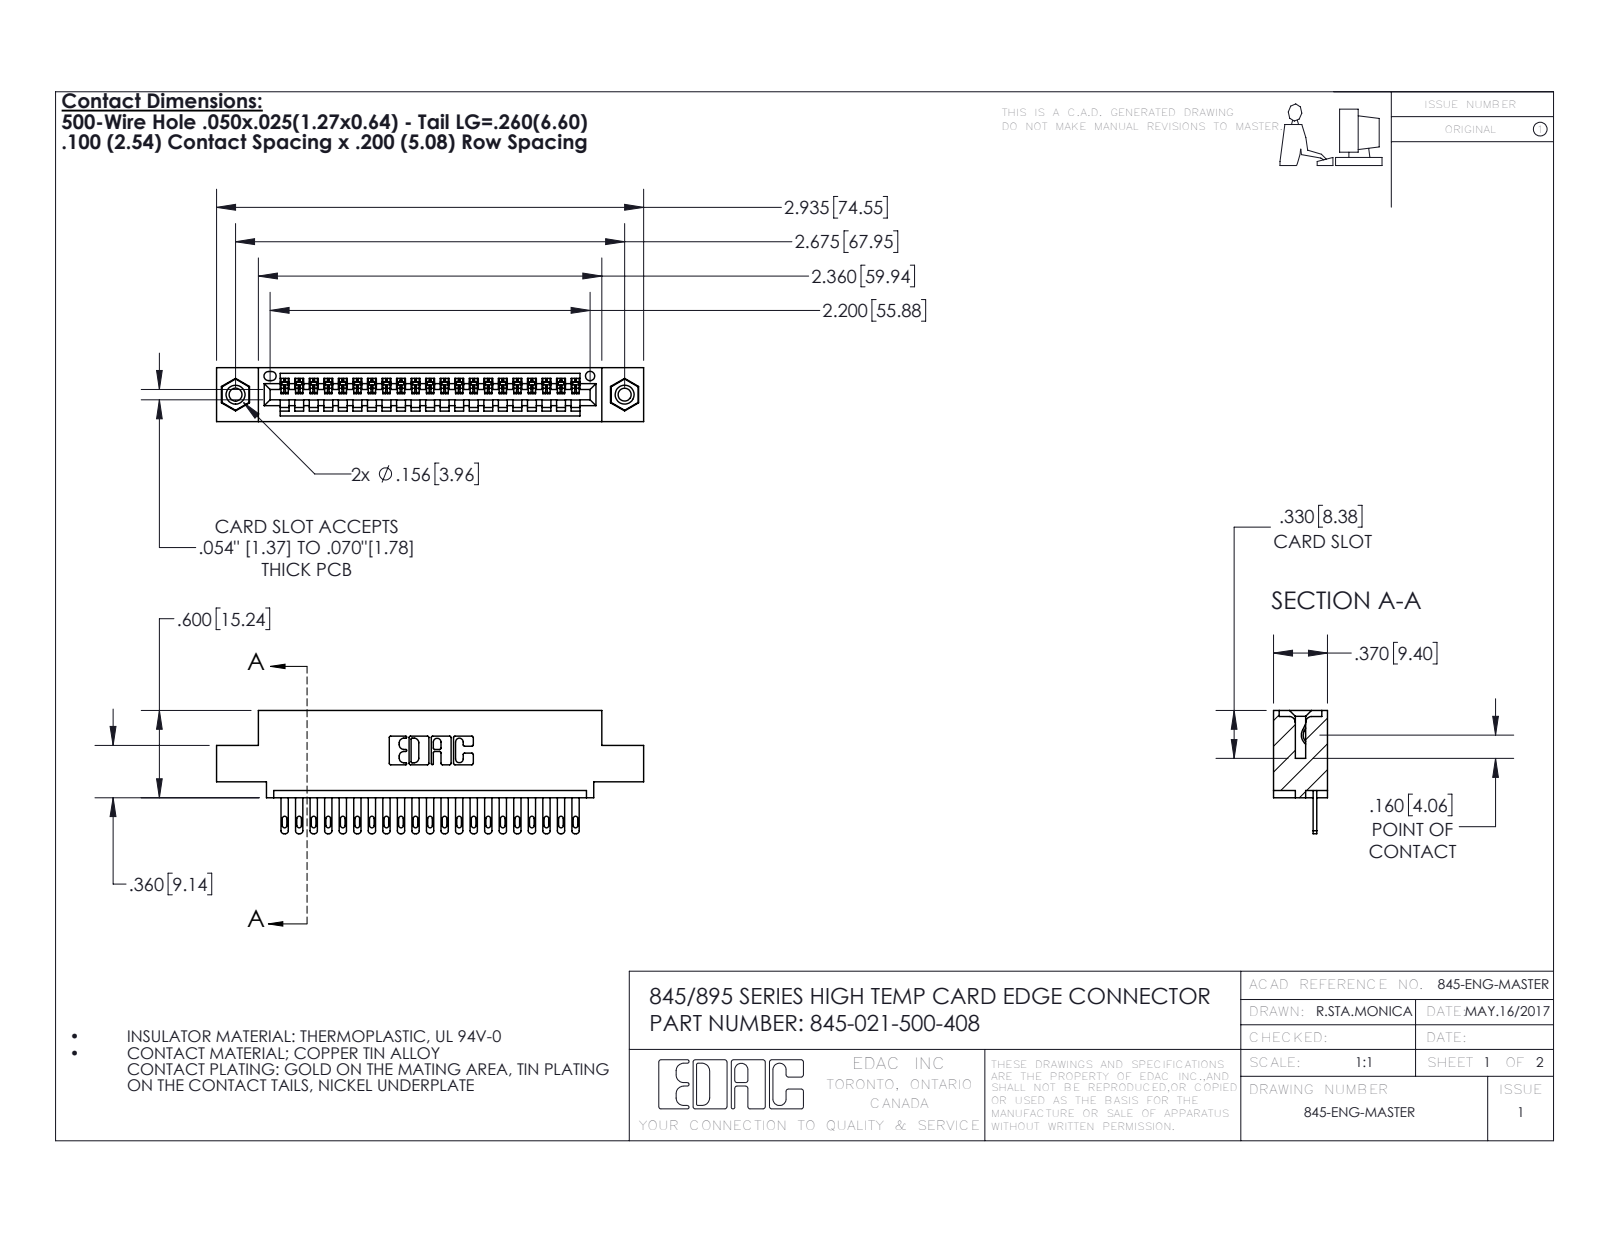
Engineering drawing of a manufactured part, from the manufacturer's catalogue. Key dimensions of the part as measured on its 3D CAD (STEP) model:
Part name (STEP PRODUCT): 345-292-001_345-293-100; 345-021-500-408; 345 Part_0.110 Offset - 0.156 Dia-TI; 345-250-001_345-250-003-102
STEP written by: SolidWorks 2016 (CONFIG_CONTROL_DESIGN)
Units: inches
Bodies: 24 solids, 1324 faces (830 planar, 478 cylindrical, 16 other)
Overall size (bounding box): 2.935 × 0.847 × 0.37
Volume: 0.418 in³ · Surface area: 13.88 in²
Round holes (diameter × count): ⌀0.089 ×2, ⌀0.125 ×2, ⌀0.156 ×2, ⌀0.064 ×1
Round bosses / shafts (diameter × count): ⌀0.155 ×2
Partial cylindrical surfaces — rounded edges, fillets, slot ends (radius × count): R0.006 ×42, R0.016 ×42, R0.02 ×42, R0.01 ×22, R0.007 ×6, R0.031 ×6, R0.026 ×3, R0.031 ×2
Main face-to-face distances: 0.072, 0.298, 0.2, 0.37, 0.098, 0.272, 0.025, 0.225, 0.149, 0.072
Hole centre spacings: 0.27, 2.441, 2.675
